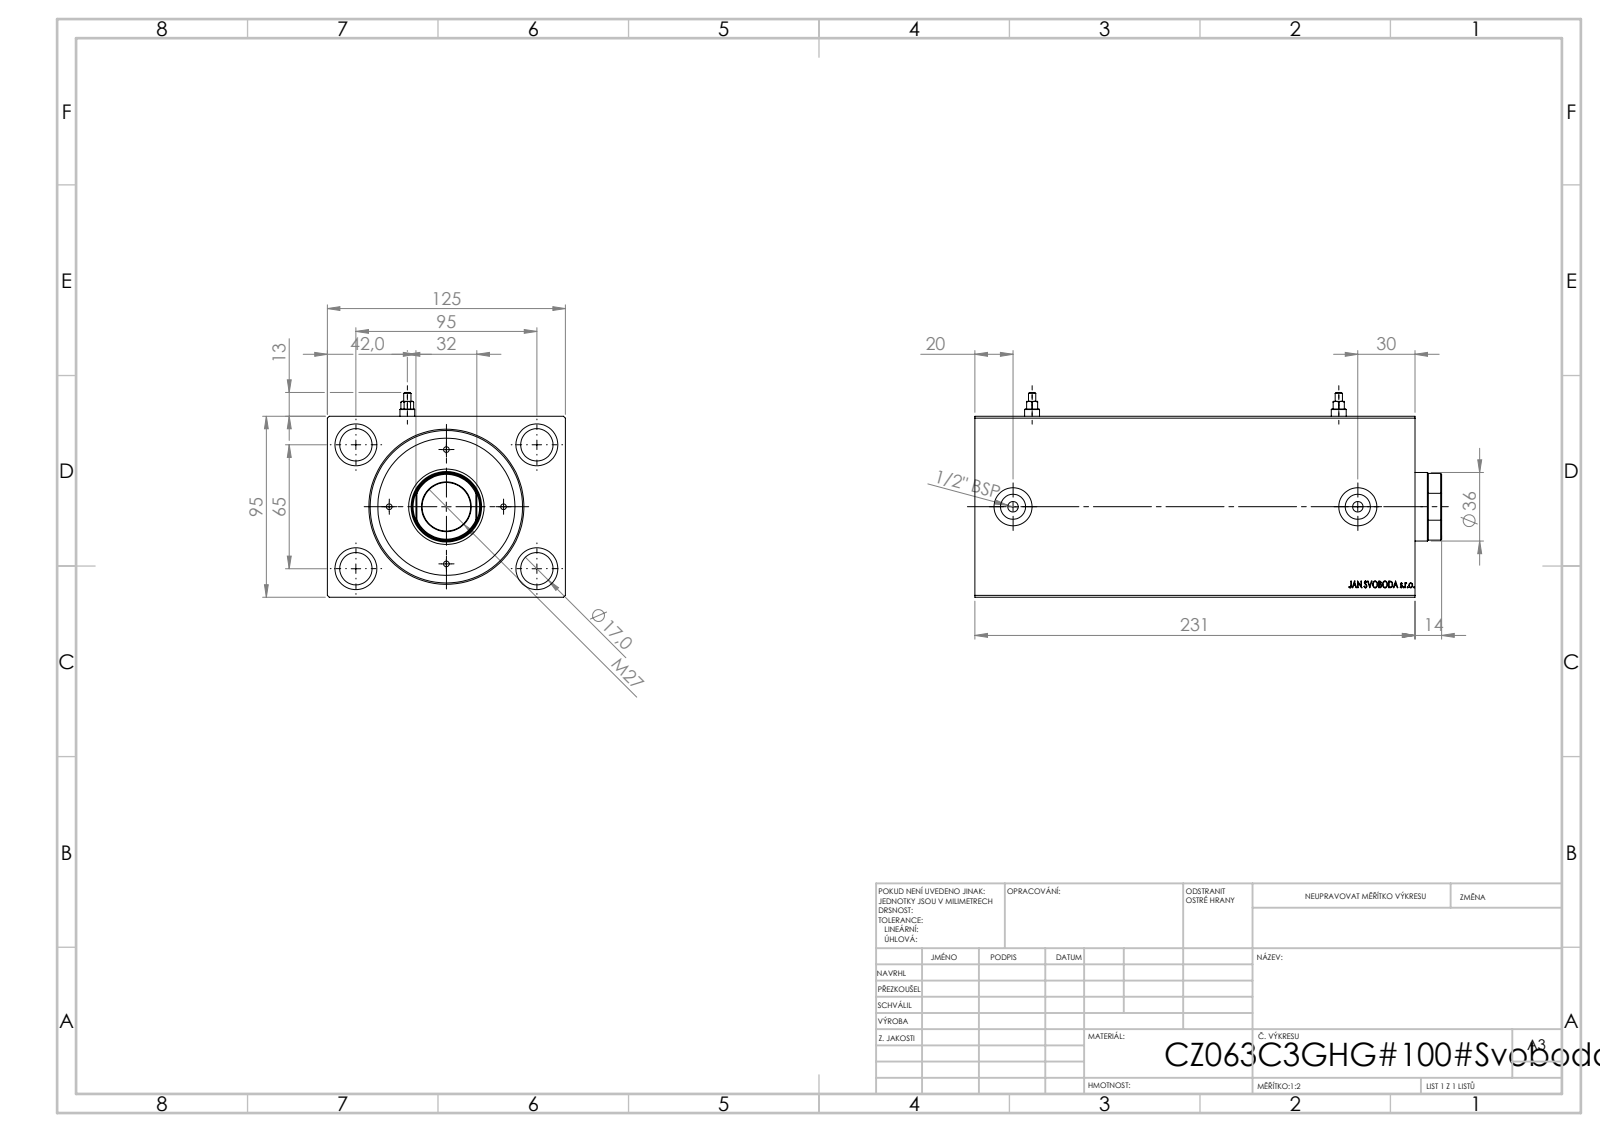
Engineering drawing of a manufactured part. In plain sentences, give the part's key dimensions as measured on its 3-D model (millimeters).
Its 3-D file was written by "SolidWorks 2019 (CONFIG_CONTROL_DESIGN)". It is 1 solid with 825 faces: 397 planar, 46 cylindrical and 382 other. Overall it measures 231 by 125 by 95 millimeters. Its volume is 1 834 000 cubic millimeters and its surface area 217 517 square millimeters. Round holes: 4 of diameter 17, 4 of diameter 22, 2 of diameter 5.5, 2 of diameter 8, 2 of diameter 13.16, 2 of diameter 20, 1 of diameter 36, 1 of diameter 63, 1 of diameter 80. The main face-to-face distances are 95, 125, 231, 210.2, 20.8, 14, 196.2, 217, 10.33, 220.67. The hole center spacings are 57.55, 65, 95, 115.11, 161, 181.
